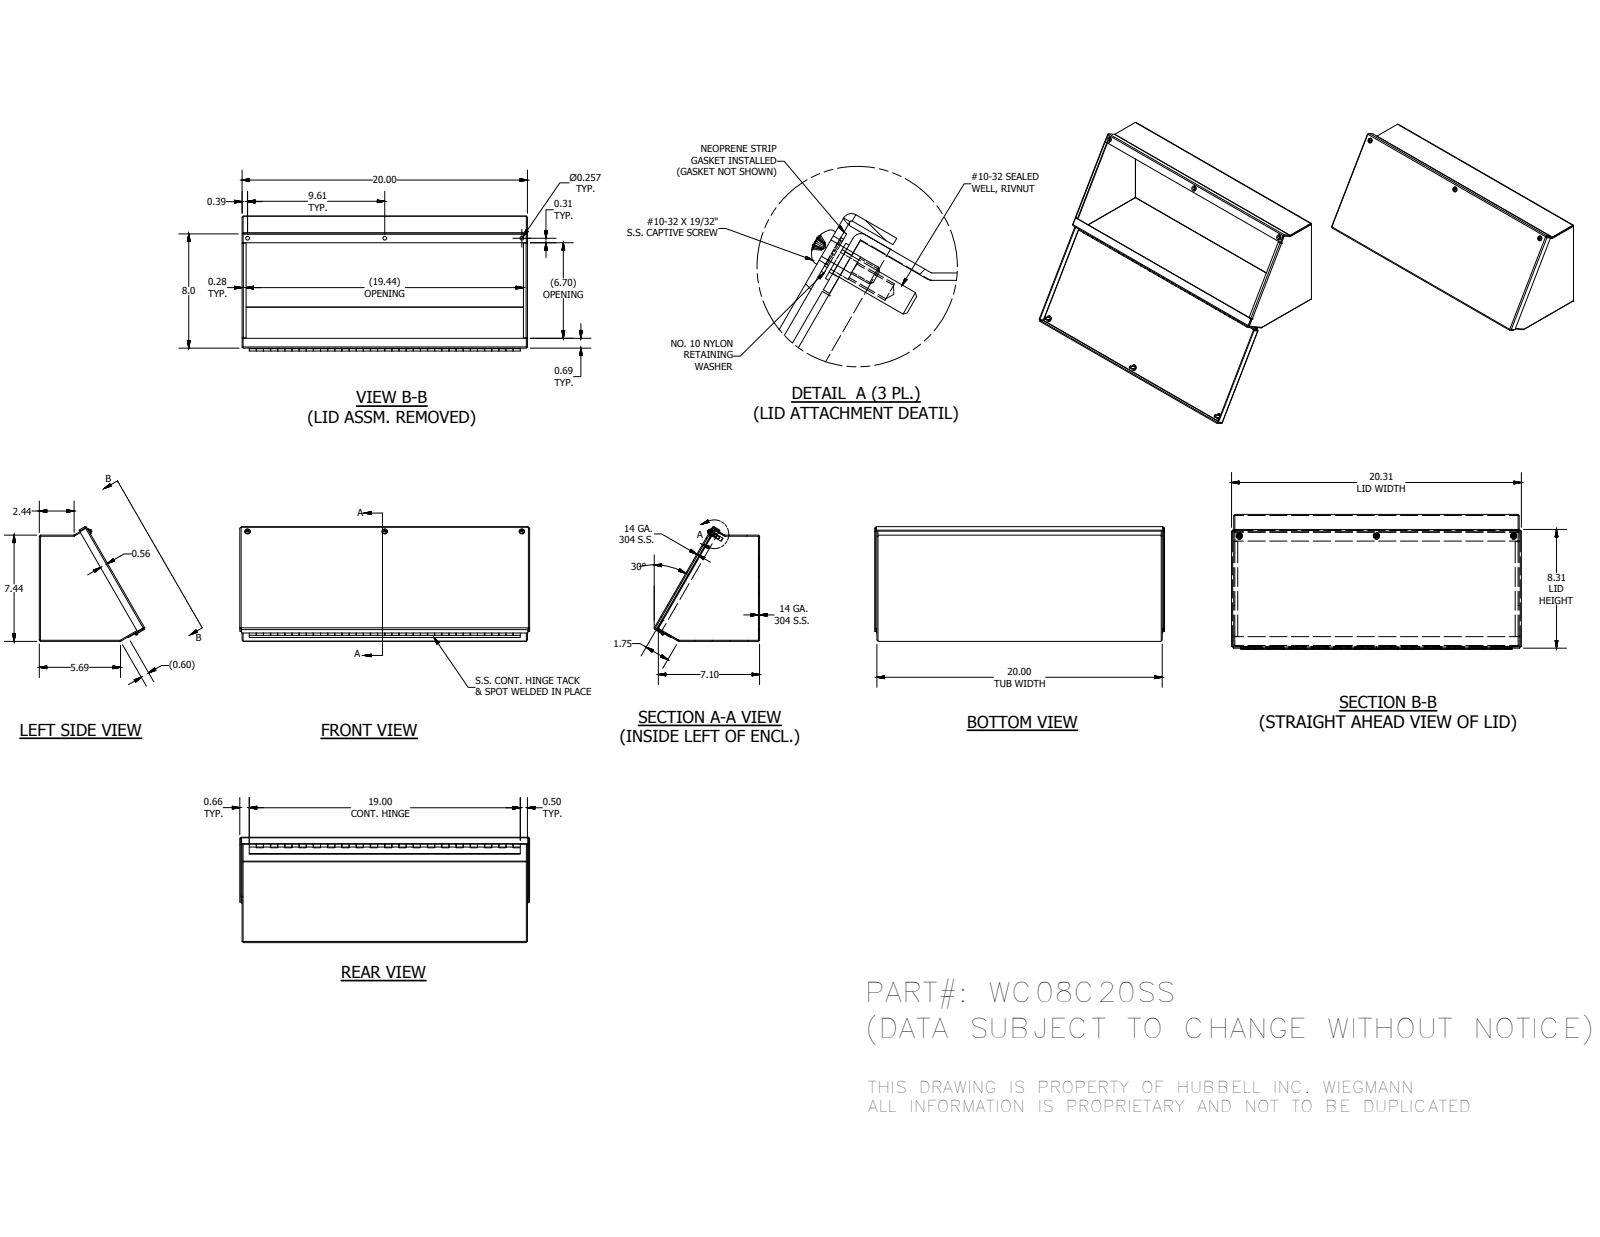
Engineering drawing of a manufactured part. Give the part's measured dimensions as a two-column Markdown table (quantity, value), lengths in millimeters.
| quantity | value |
| --- | --- |
| part name | WC08C20SSBTB; WC08C20SSLID; WC08CSSLS; WC08CSSRS (+8 more) |
| STEP written by | Autodesk Inventor 2014 (AUTOMOTIVE_DESIGN) |
| units | millimeters |
| bodies | 16 solids, 557 faces (340 planar, 143 cylindrical, 74 other) |
| overall size | 515.94 × 204.03 × 187.63 |
| volume | 820 374 mm³ |
| surface area | 903 138 mm² |
| round holes (diameter × count) | 3.96 × 3, 4.98 × 3, 6.53 × 3, 7.06 × 3, 7.14 × 3, 2.96 × 1 |
| round bosses / shafts (diameter × count) | 11.51 × 3, 10.31 × 3, 9.47 × 3, 6.3 × 3, 4.83 × 3, 5.08 × 1, 2.54 × 1 |
| partial cylindrical surfaces (radius × count) | 0.4 × 12, 2.28 × 12, 2.27 × 3 |
| main face-to-face distances | 1.88, 187.03, 506.12, 185.15, 188.91, 504.24, 508, 2.94, 203.1, 1.06 |
| hole center spacings | 244.17, 244.18, 488.34, 1.62 |
